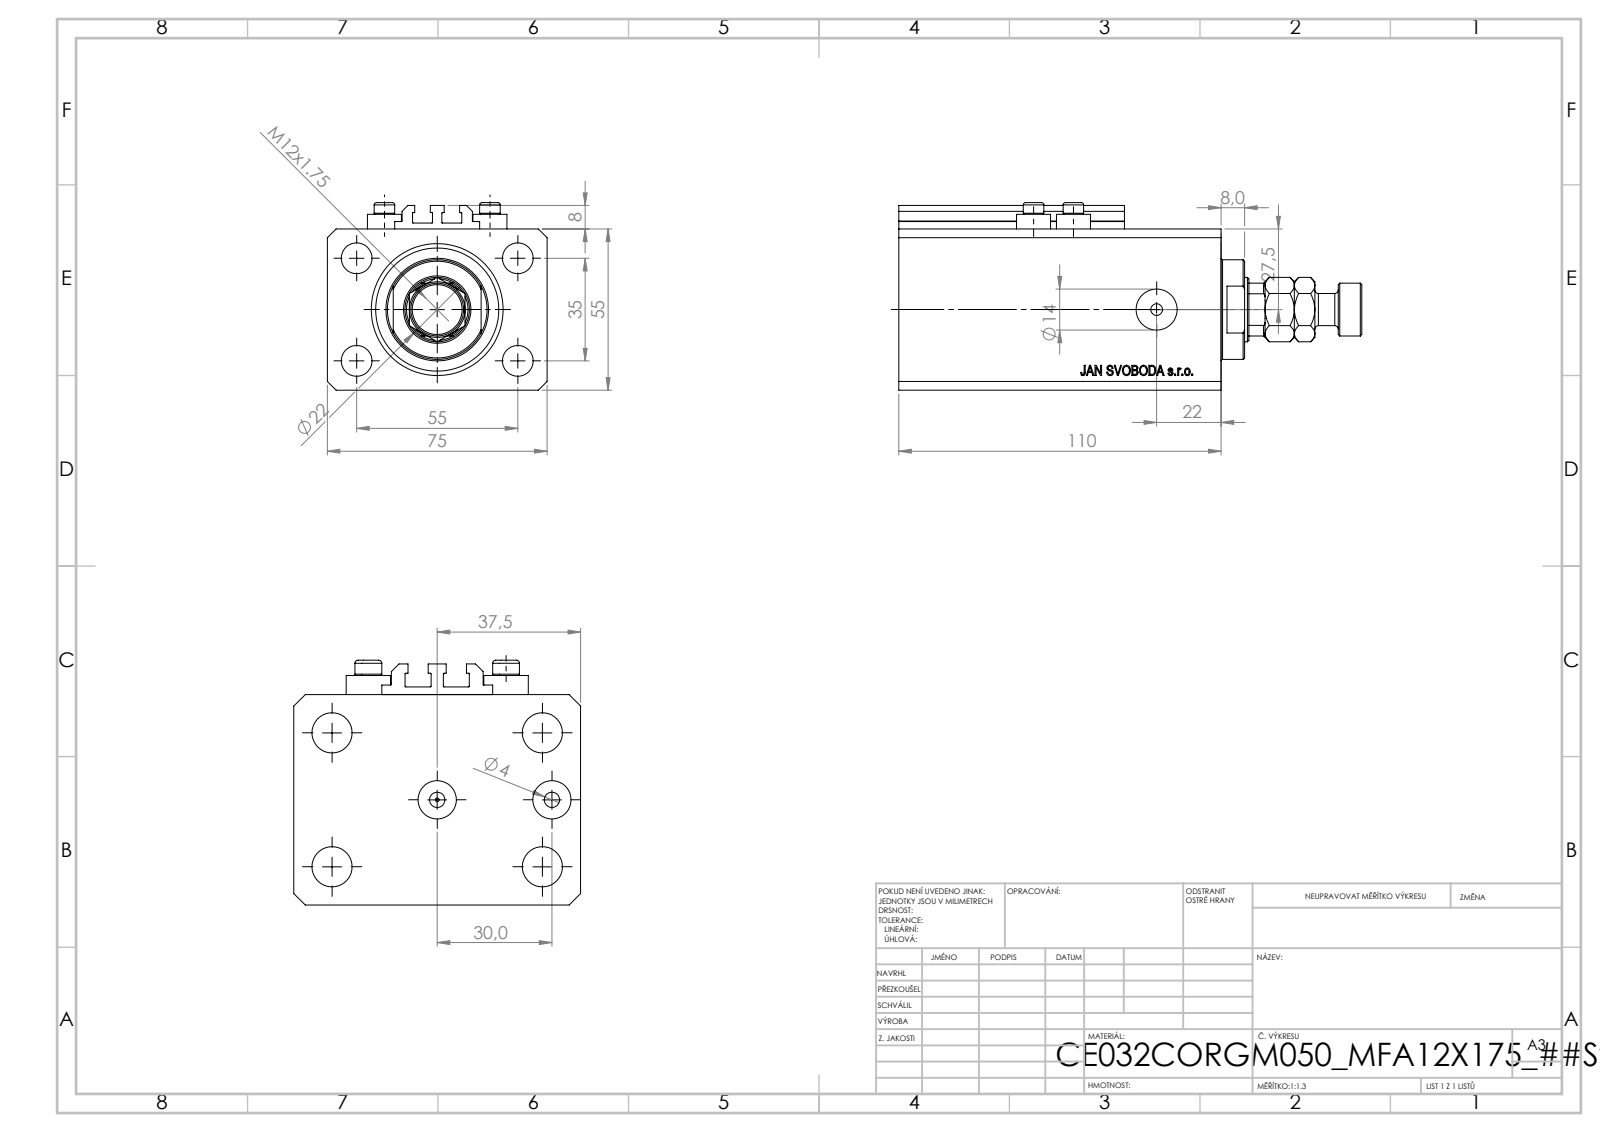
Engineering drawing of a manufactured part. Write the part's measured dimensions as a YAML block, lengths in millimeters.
part_name: "V250CE_C_VCP; MFA; V250CE_C_Body; ALLEN BOLT V250CE (+1 more)"
step_written_by: "SolidWorks 2019 (CONFIG_CONTROL_DESIGN)"
units: millimeters
bodies: {solids: 9, faces: 1090, planar: 520, cylindrical: 92, other: 478}
overall_size: [158, 75, 64]
volume: 416515
surface_area: 94305
round_holes:
  - {diameter: 4, count: 8}
  - {diameter: 10.5, count: 5}
  - {diameter: 10, count: 2}
  - {diameter: 14, count: 2}
  - {diameter: 1.25, count: 1}
  - {diameter: 22, count: 1}
  - {diameter: 32, count: 1}
  - {diameter: 45, count: 1}
round_bosses_or_shafts:
  - {diameter: 11.6, count: 4}
  - {diameter: 7, count: 4}
  - {diameter: 34, count: 1}
  - {diameter: 18, count: 1}
  - {diameter: 11, count: 1}
partial_cylinders:
  - {radius: 0.2, count: 10}
  - {radius: 10.5, count: 1}
face_to_face_distances: [55, 75, 110, 15, 95, 9.9, 85.1, 100.1, 2.5, 8]
hole_center_spacings: [32.6, 13.6, 17.68, 35, 36, 38.48, 55, 60.1]
